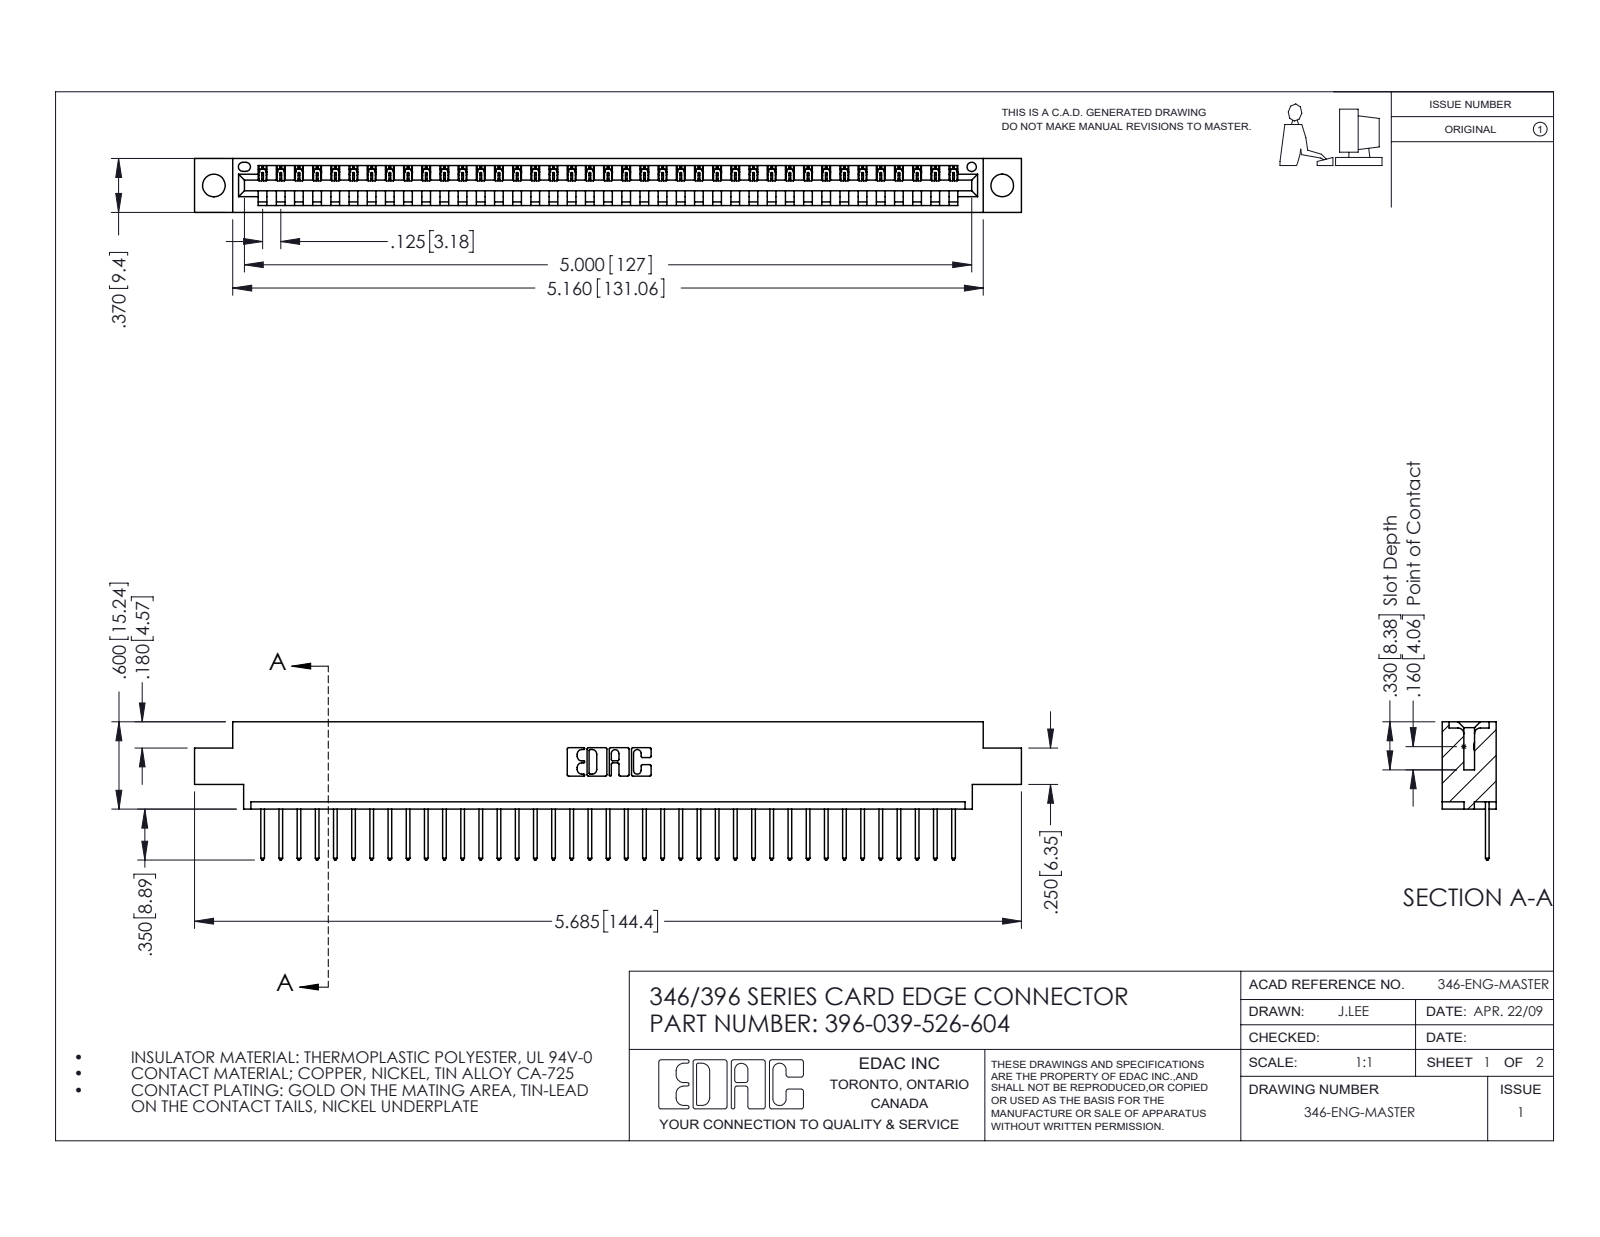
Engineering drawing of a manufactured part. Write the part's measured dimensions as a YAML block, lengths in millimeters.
part_name: "345-292-001_345-293-126; 346 Part_0.170 Offset - 0.156 Dia-TH; 396-039-526-604"
step_written_by: "SolidWorks 2016 (CONFIG_CONTROL_DESIGN)"
units: millimeters
bodies: {solids: 40, faces: 2388, planar: 1640, cylindrical: 748, other: 0}
overall_size: [144.4, 24.1, 9.4]
volume: 13500
surface_area: 16800
round_holes:
  - {diameter: 4, count: 2}
  - {diameter: 1.6, count: 1}
partial_cylinders:
  - {radius: 0.2, count: 78}
  - {radius: 0.3, count: 78}
  - {radius: 0.3, count: 22}
  - {radius: 0.2, count: 6}
  - {radius: 0.8, count: 6}
  - {radius: 0.7, count: 3}
  - {radius: 0.8, count: 2}
  - {radius: 1, count: 2}
face_to_face_distances: [1.2, 8.2, 9.4, 6.4, 1.8, 7.6, 0.6, 3.8, 5.6, 2.5]
hole_center_spacings: [6.2, 132.4, 137.7]
